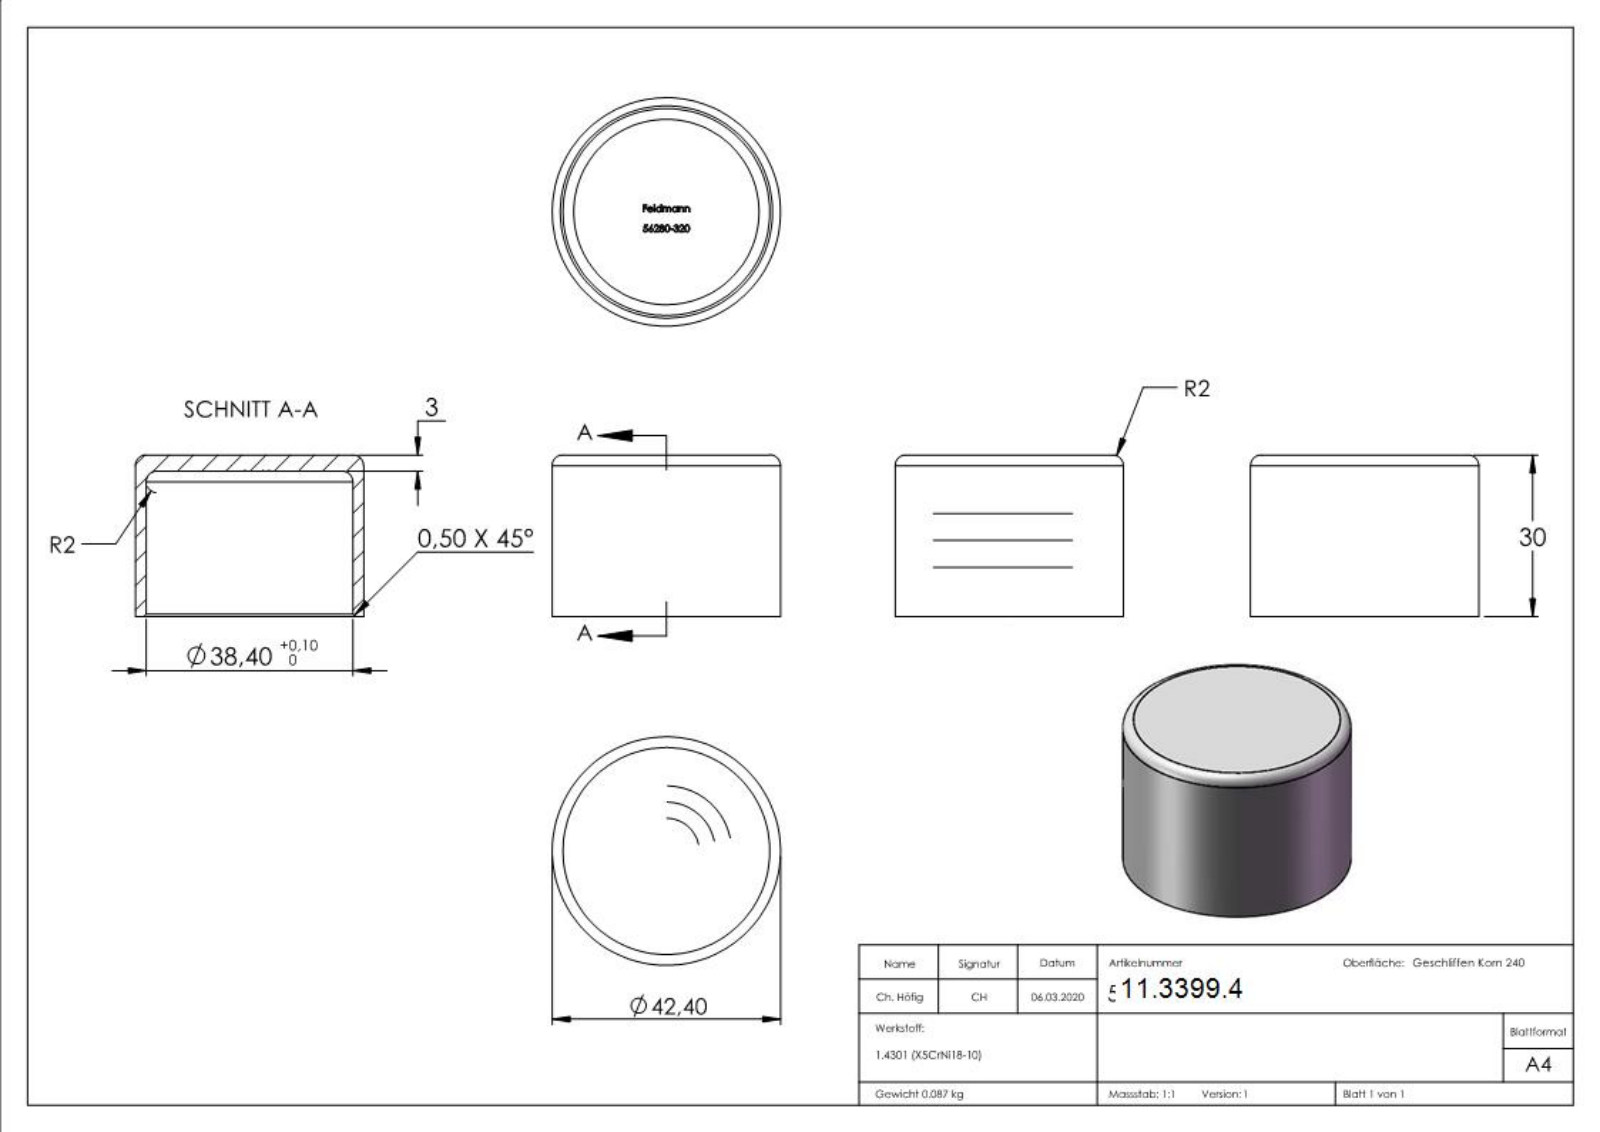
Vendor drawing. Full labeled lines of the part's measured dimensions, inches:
Part name (STEP PRODUCT): 56280-320
STEP written by: SolidWorks 2015 (CONFIG_CONTROL_DESIGN)
Units: inches
Bodies: 1 solid, 241 faces (110 planar, 2 cylindrical, 129 other)
Overall size (bounding box): 1.669 × 1.669 × 1.181
Volume: 0.675 in³ · Surface area: 15.24 in²
Round holes (diameter × count): ⌀1.512 ×1
Round bosses / shafts (diameter × count): ⌀1.669 ×1
Main face-to-face distances: 0.118, 1.063, 1.181, 1.067, 0.114, 0.015, 0.117, 0.044, 0.146, 0.161
